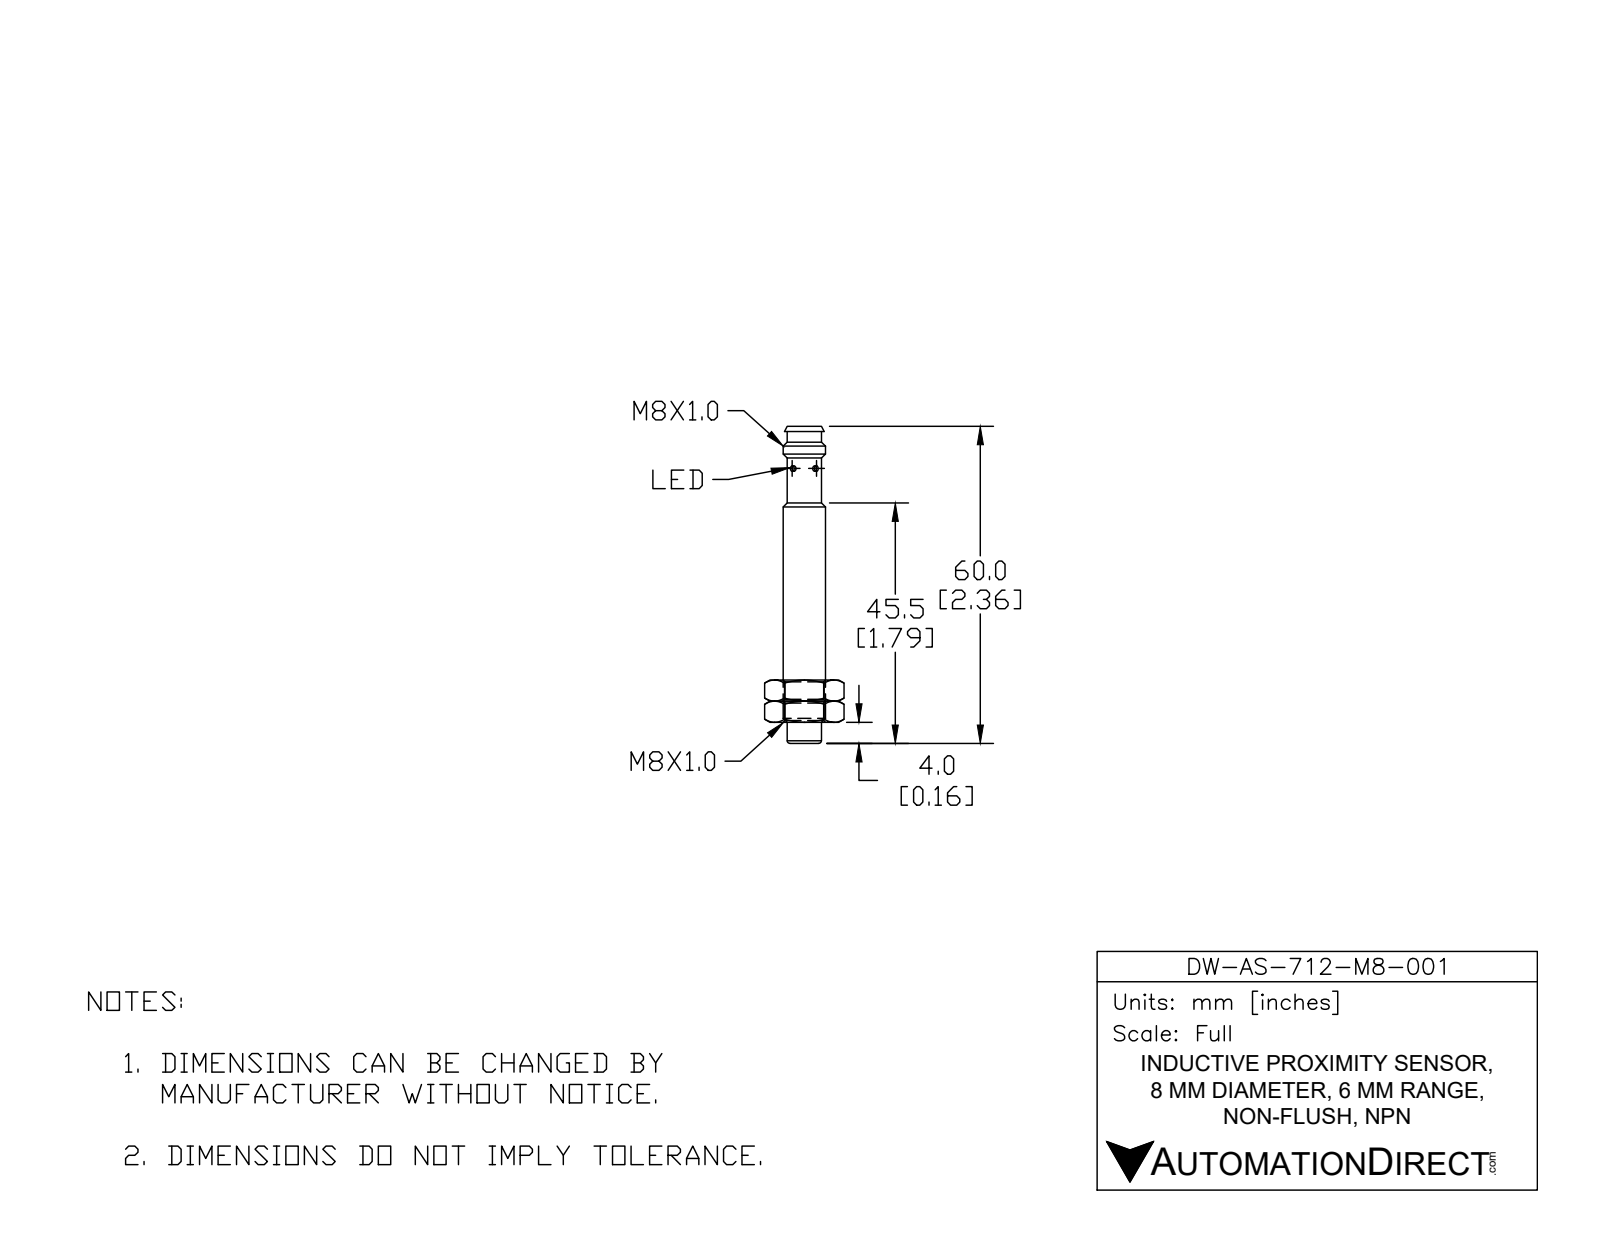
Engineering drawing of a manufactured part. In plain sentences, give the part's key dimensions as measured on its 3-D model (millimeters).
The part is named "DW-AS-712-M8-001". Its 3-D file was written by "SolidWorks 2017 (AUTOMOTIVE_DESIGN)". It is 1 solid with 49 faces: 15 planar, 22 cylindrical and 12 other. Overall it measures 60 by 8 by 8 millimeters. Its volume is 2 620 cubic millimeters and its surface area 1 686 square millimeters. Round holes: 2 of diameter 1.8. Round bosses or shafts: 3 of diameter 1, 1 of diameter 8, 1 of diameter 6.9, 1 of diameter 6.5, 1 of diameter 6. Partial cylindrical surfaces (rounded edges, fillets, slot ends): 1 of radius 3. The main face-to-face distances are 55.3, 4, 60, 4.6, 50.9, 4.5, 9.1.
